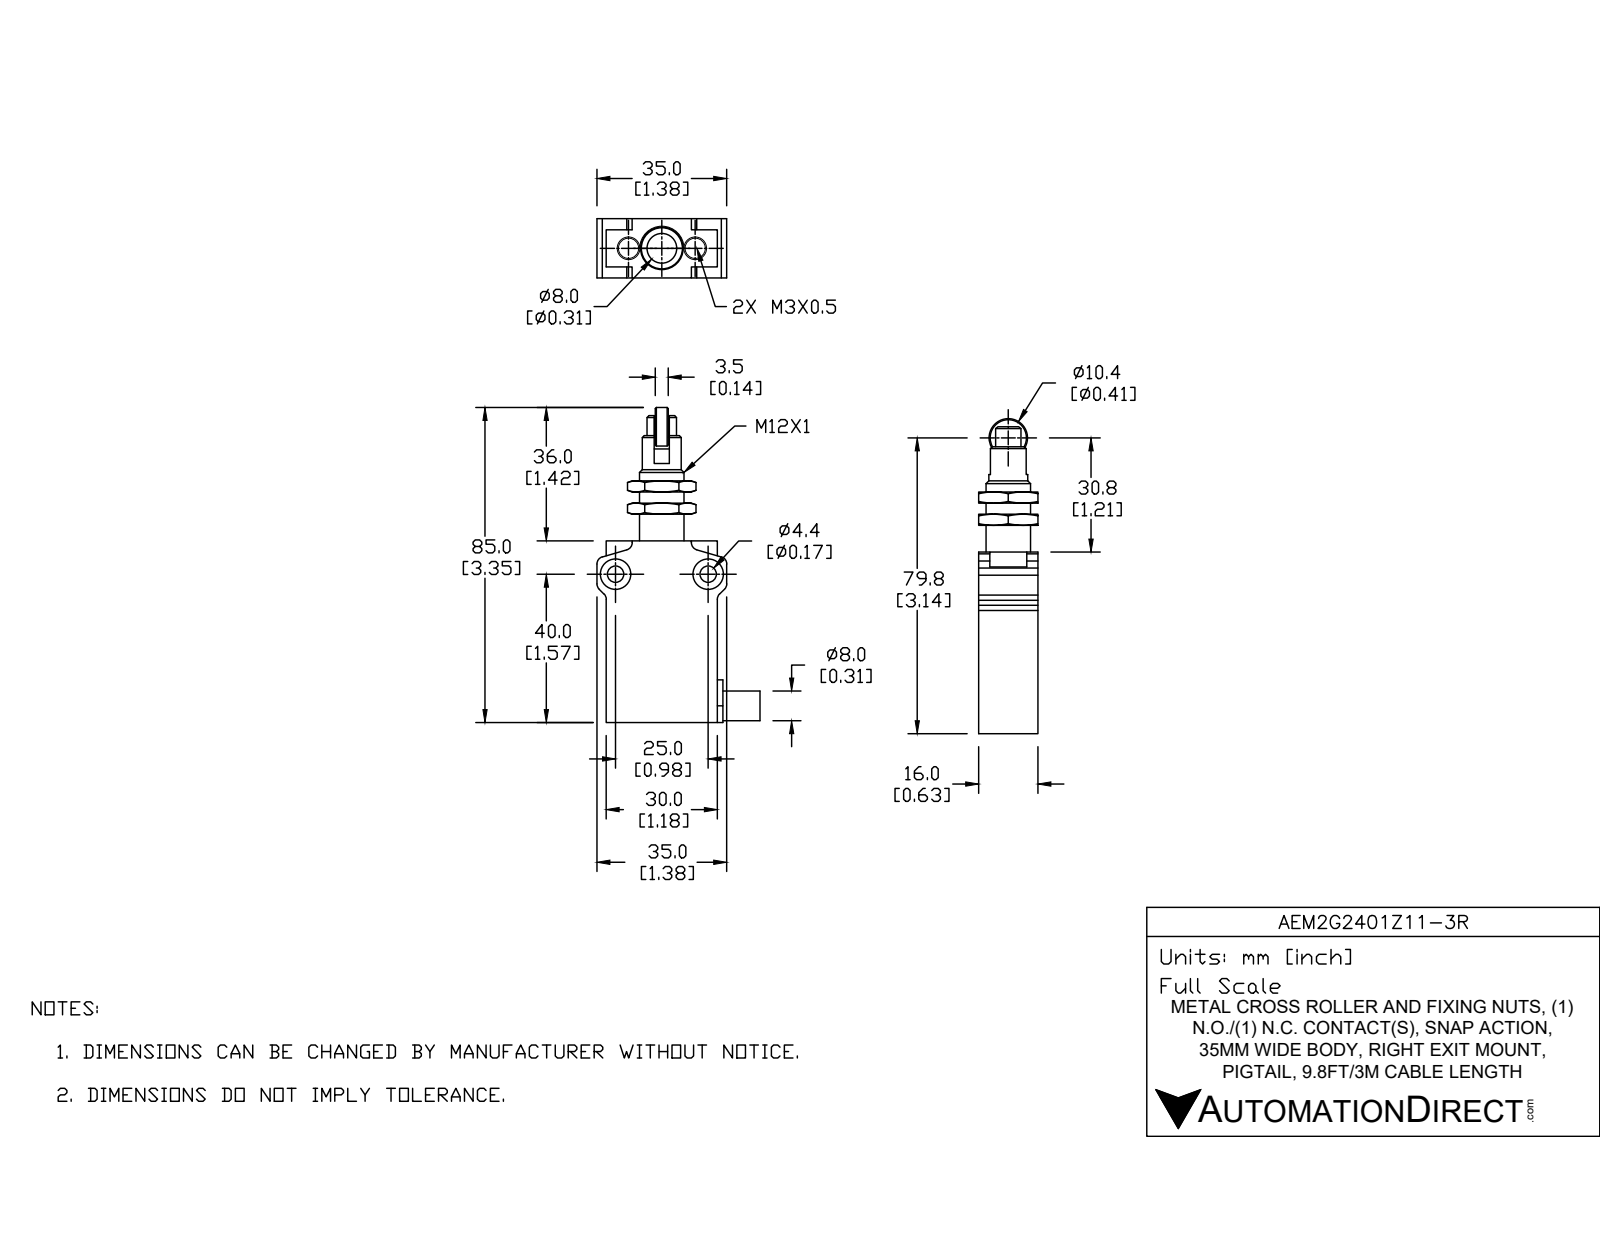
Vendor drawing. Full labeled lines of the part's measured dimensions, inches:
Part name (STEP PRODUCT): AEM2G2401Z11-3R
STEP written by: SolidWorks 2017 (AUTOMOTIVE_DESIGN)
Units: inches
Bodies: 7 solids, 178 faces (79 planar, 56 cylindrical, 43 other)
Overall size (bounding box): 3.346 × 1.87 × 0.727
Volume: 1.658 in³ · Surface area: 17.53 in²
Round holes (diameter × count): ⌀0.118 ×2, ⌀0.173 ×2, ⌀0.323 ×2, ⌀0.317 ×1, ⌀0.472 ×1
Round bosses / shafts (diameter × count): ⌀0.413 ×1, ⌀0.409 ×1, ⌀0.323 ×1, ⌀0.313 ×1, ⌀0.22 ×1
Partial cylindrical surfaces — rounded edges, fillets, slot ends (radius × count): R0.079 ×8, R0.256 ×1
Main face-to-face distances: 0.63, 1.181, 0.472, 0.118, 0.236, 1.929, 1.74, 0.189, 0.354, 0.157
Hole centre spacings: 0.374, 0.748, 0.984
